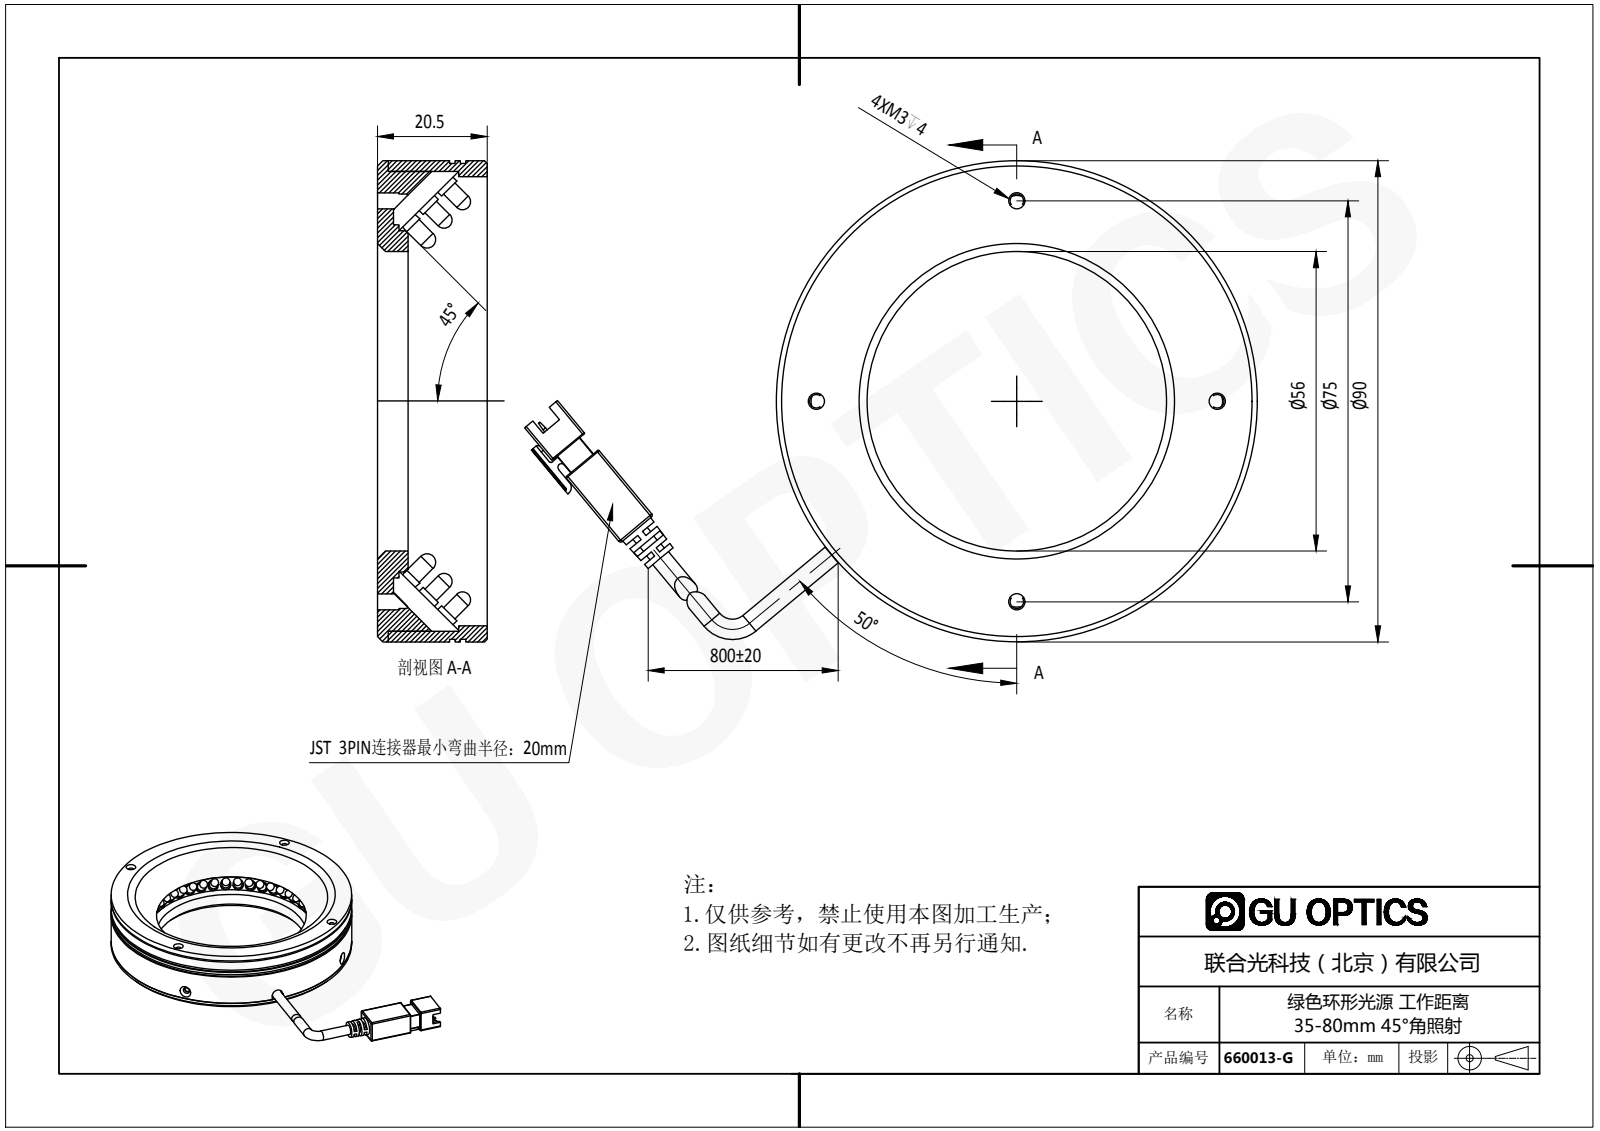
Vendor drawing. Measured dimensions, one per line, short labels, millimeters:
name: 660013-G
written by: SolidWorks 2016 (AUTOMOTIVE_DESIGN)
unit: mm
bodies: 156 solids, 2970 faces (1958 planar, 768 cylindrical, 244 other)
size: 141.36 × 95.39 × 24.5
volume: 48 891 mm³; area: 57 279 mm²
holes: 4× ⌀1.25, 4× ⌀1.6, 4× ⌀1.8, 4× ⌀2, 4× ⌀3, 3× ⌀3.5, 2× ⌀2.4, 1× ⌀56, 1× ⌀84
bosses: 150× ⌀3.8, 150× ⌀3, 2× ⌀3.5, 1× ⌀90, 1× ⌀89, 1× ⌀86, 1× ⌀66, 1× ⌀63.8
rounds: 15× R0.1, 13× R0.2, 12× R0.4, 4× R1.25, 1× R0.3, 1× R0.68, 1× R1.4, 1× R1.6
face distances: 2, 20.5, 1, 22.5, 18.5, 3, 14.8, 3.7, 5.7, 16.8
hole spacings: 56.68, 3.99, 5, 6.64, 37.5, 42.5, 53.03, 60.1
